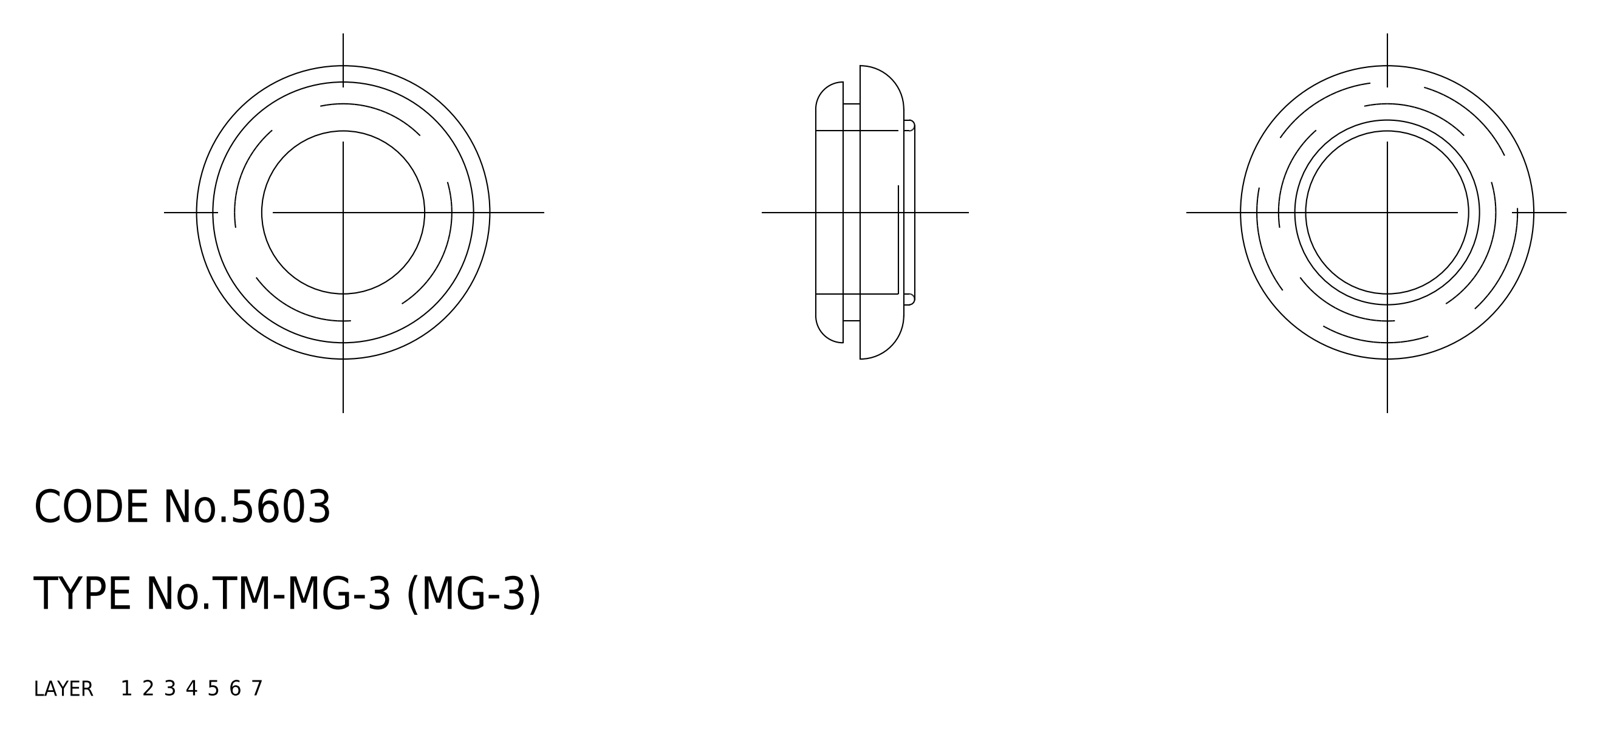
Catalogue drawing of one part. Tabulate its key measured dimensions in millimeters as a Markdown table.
| quantity | value |
| --- | --- |
| STEP written by | spGate 15.6.1 (AUTOMOTIVE_DESIGN) |
| units | millimeters |
| bodies | 1 solid, 24 faces (6 planar, 12 cylindrical, 6 other) |
| overall size | 27 × 27 × 9.1 |
| volume | 2 455 mm³ |
| surface area | 2 342 mm² |
| round holes (diameter × count) | 15 × 1 |
| round bosses / shafts (diameter × count) | 27 × 1, 24 × 1, 20 × 1, 17 × 1 |
| main face-to-face distances | 4, 4.1, 8.1, 7.6, 3.5, 0.5, 2.5, 1.6, 5.1, 5.6 |
